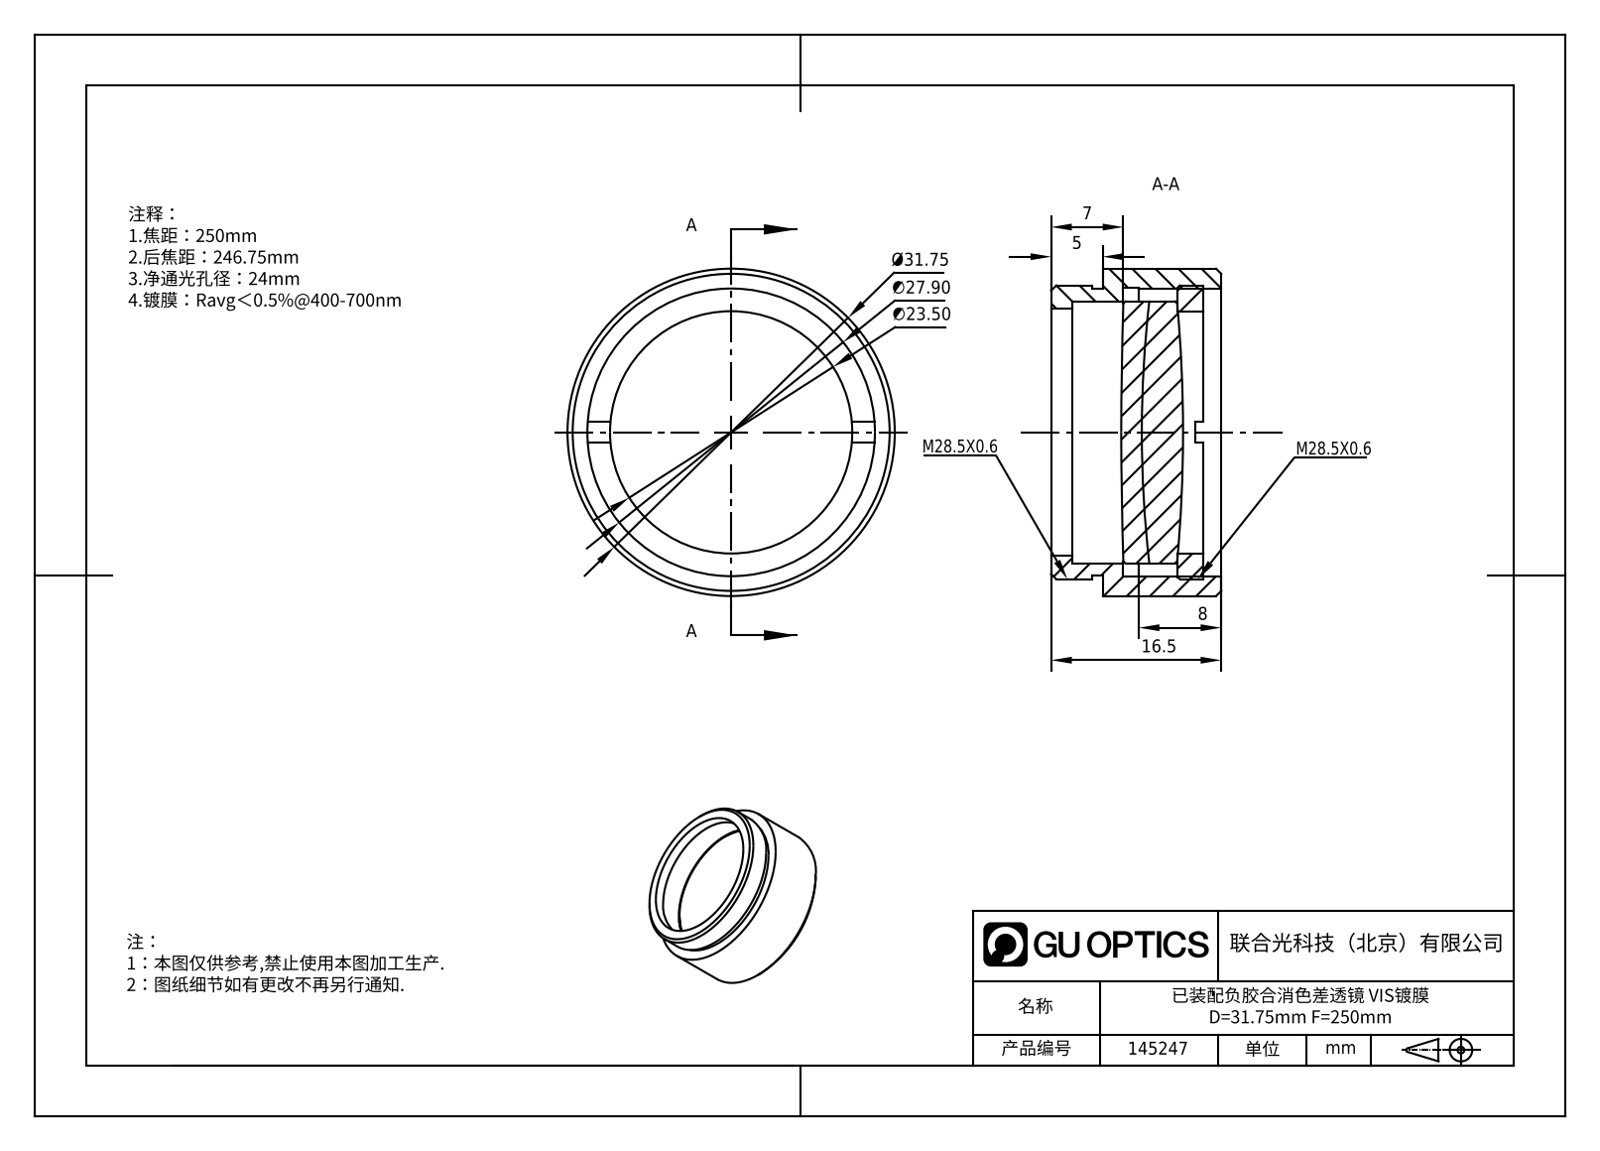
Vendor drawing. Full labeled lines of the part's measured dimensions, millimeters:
Part name (STEP PRODUCT): M28.5x0.6安装环PN35020-LM254-D1; GL31-025B-250-VIS_Solidworks; M28.5x0.6ѹȦ; APD-ML25-250-VIS
STEP written by: SolidWorks 2022 (AUTOMOTIVE_DESIGN)
Units: millimetres
Bodies: 4 solids, 56 faces (16 planar, 22 cylindrical, 18 other)
Overall size (bounding box): 31.76 × 31.76 × 16.5
Volume: 6 323 mm³ · Surface area: 6 907 mm²
Round holes (diameter × count): ⌀23.5 ×1, ⌀24 ×1, ⌀27.9 ×1, ⌀28 ×1
Round bosses / shafts (diameter × count): ⌀31.76 ×1, ⌀28.5 ×1, ⌀27.8 ×1, ⌀25.4 ×1
Main face-to-face distances: 2, 5, 2.5, 7.29, 9.79, 12.29, 14.79, 16.5, 11.5, 4.21
